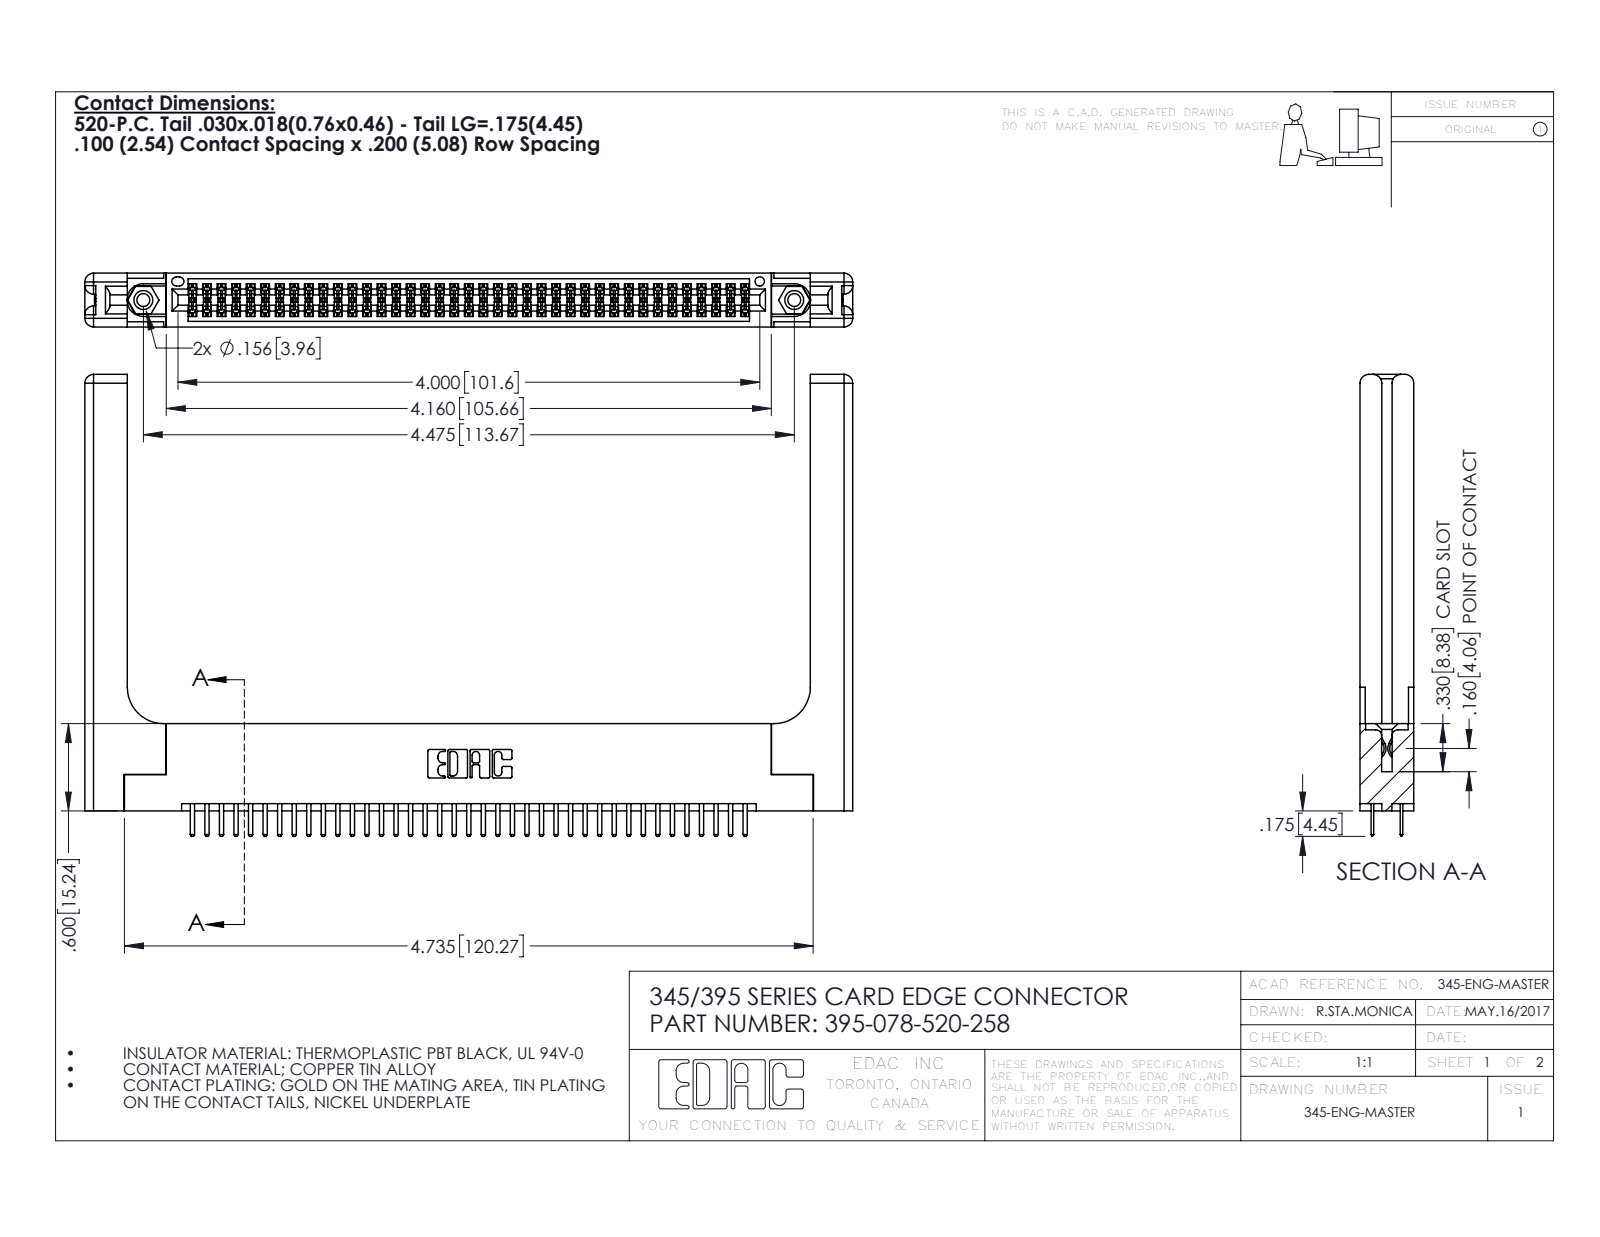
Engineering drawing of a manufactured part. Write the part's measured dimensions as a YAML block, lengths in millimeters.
part_name: "345 Part_Flush Mounting Lugs - 0.156 Dia-TH; 345-250-001_345-250-001-102; 395-078-520-258; 345-220-058_345-220-058 (+1 more)"
step_written_by: "SolidWorks 2016 (CONFIG_CONTROL_DESIGN)"
units: millimeters
bodies: {solids: 83, faces: 4594, planar: 2958, cylindrical: 1576, other: 60}
overall_size: [134.1, 80.6, 9.4]
volume: 21430
surface_area: 24090
round_holes:
  - {diameter: 2.3, count: 2}
  - {diameter: 3.2, count: 2}
  - {diameter: 4, count: 2}
  - {diameter: 1.6, count: 1}
round_bosses_or_shafts:
  - {diameter: 3.9, count: 2}
partial_cylinders:
  - {radius: 0.2, count: 117}
  - {radius: 0.3, count: 82}
  - {radius: 0.3, count: 22}
  - {radius: 1.5, count: 16}
  - {radius: 0.2, count: 6}
  - {radius: 0.8, count: 6}
  - {radius: 0.7, count: 3}
  - {radius: 0.4, count: 2}
face_to_face_distances: [9.4, 1.8, 7.6, 5.1, 2.5, 6.9, 0.6, 5.7, 3.8, 3.8]
hole_center_spacings: [6.9, 107.7, 113.7]
